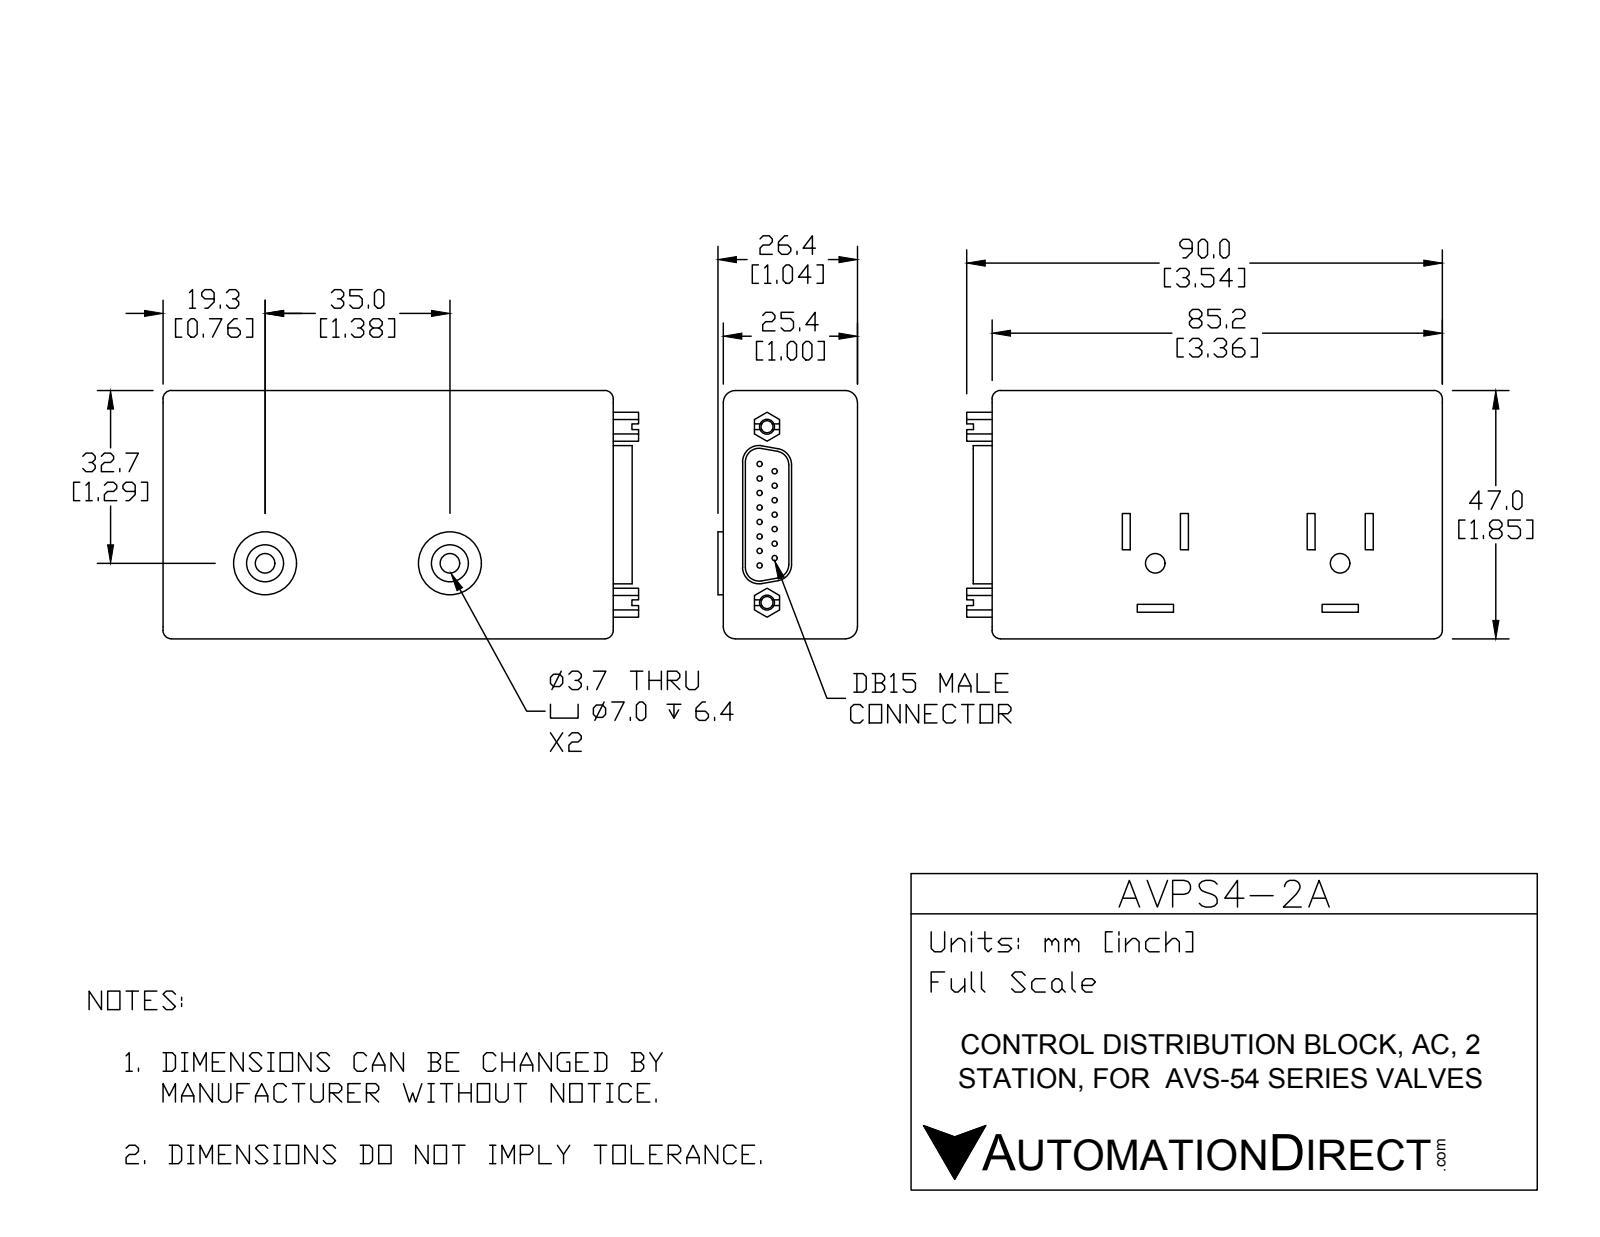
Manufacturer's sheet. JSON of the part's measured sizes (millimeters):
{"part_name": "AVPS4-2A", "step_written_by": "SolidWorks 2016 (AUTOMOTIVE_DESIGN)", "units": "millimeters", "bodies": {"solids": 1, "faces": 173, "planar": 93, "cylindrical": 68, "other": 12}, "overall_size": [90, 47, 26.4], "volume_mm3": 99850, "surface_area_mm2": 16740, "round_holes": [[2.3, 2], [3.7, 2], [7, 2]], "round_bosses_or_shafts": [[1, 15], [11.9, 2]], "partial_cylinders_radius": [[1.6, 6], [2.3, 4], [2.6, 4], [3.1, 4], [1.6, 2]], "face_to_face_distances": [25.4, 47, 85.2, 1.5, 35, 3.1, 82.1, 11, 0.5, 1], "hole_center_spacings": [33.3, 35]}
